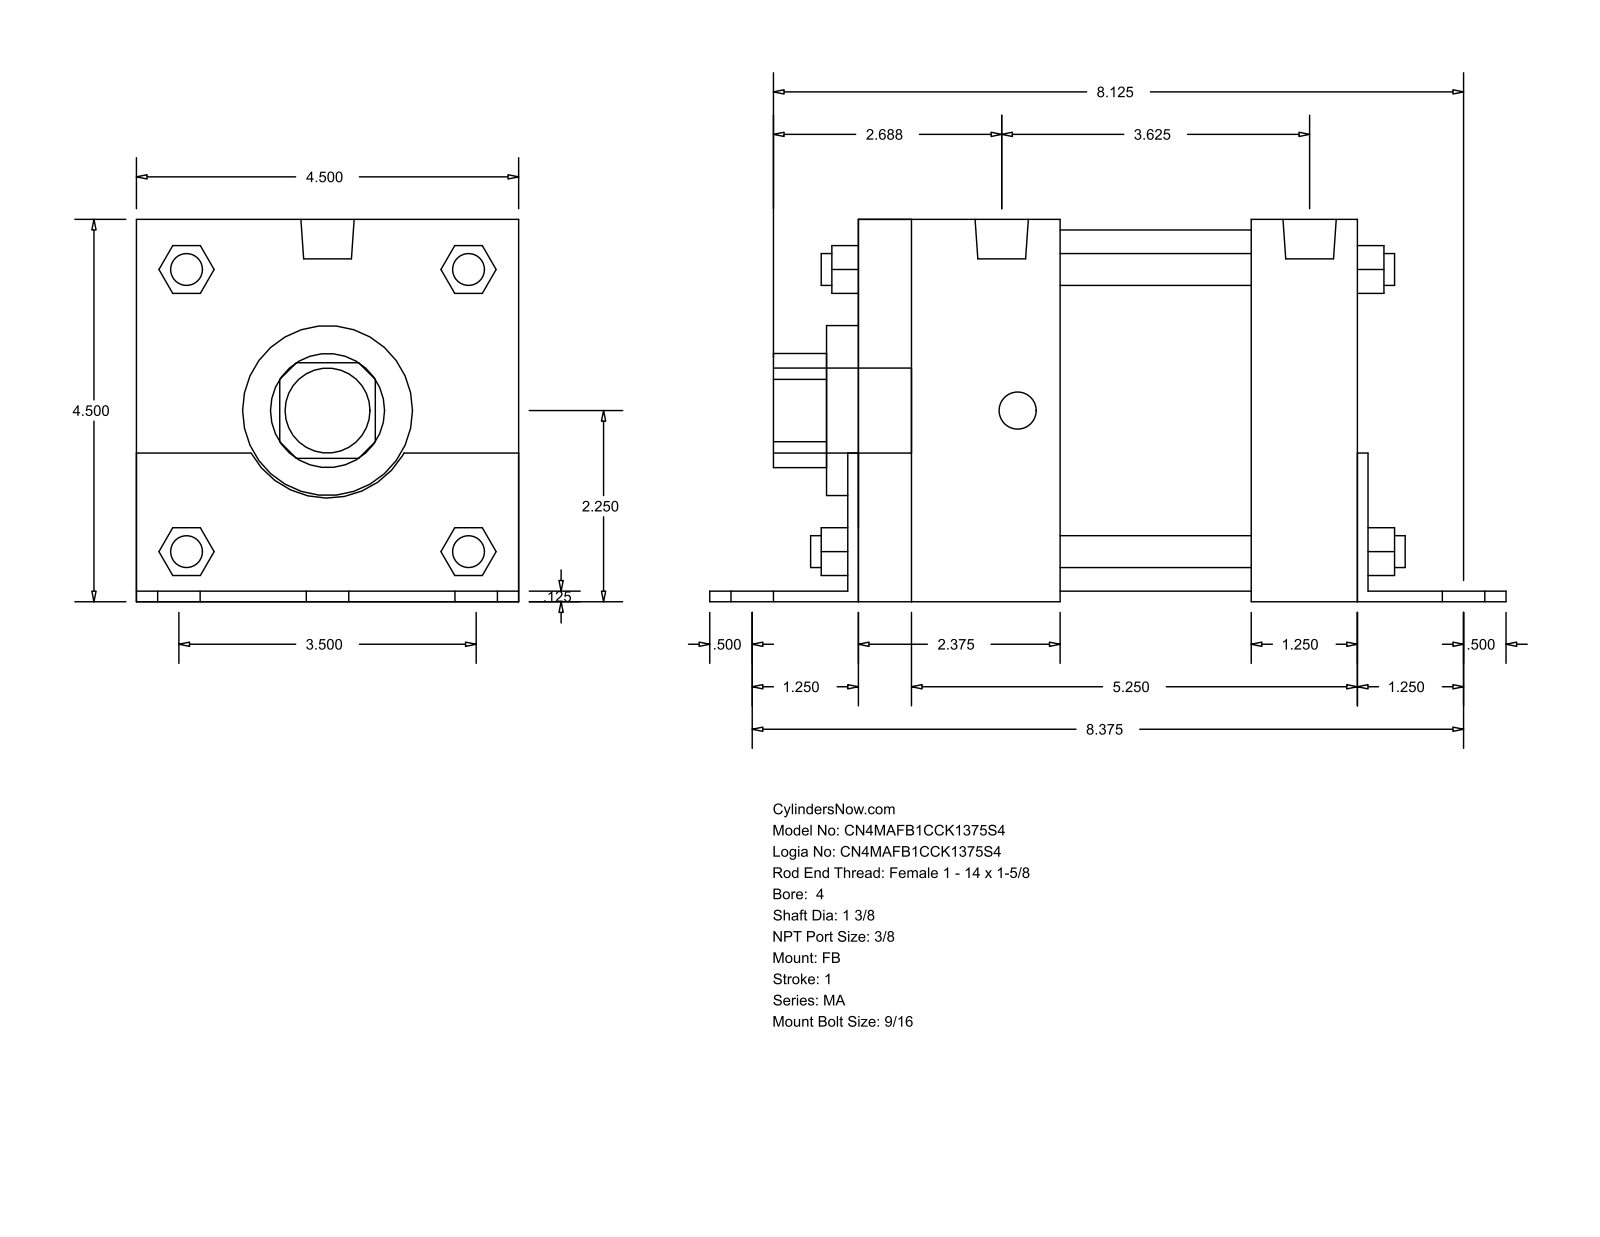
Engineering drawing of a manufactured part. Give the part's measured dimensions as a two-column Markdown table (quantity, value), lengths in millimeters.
| quantity | value |
| --- | --- |
| part name | MA_FB__0400_1.375 |
| STEP written by | GSSL Pune (CONFIG_CONTROL_DESIGN) |
| units | millimeters |
| bodies | 0 solids, 140 faces (105 planar, 35 cylindrical, 0 other) |
| overall size | 238.12 × 114.35 × 114.3 |
| round holes (diameter × count) | 34.92 × 1, 50.8 × 1, 107.95 × 1 |
| round bosses / shafts (diameter × count) | 14.29 × 6, 11.11 × 4, 9.53 × 4, 15.93 × 2, 25.4 × 1 |
| partial cylindrical surfaces (radius × count) | 17.06 × 1, 26.16 × 1 |
| main face-to-face distances | 114.3, 3.17, 114.35, 3.12, 111.18, 149.22, 3.18, 152.4, 60.32, 152.39 |
